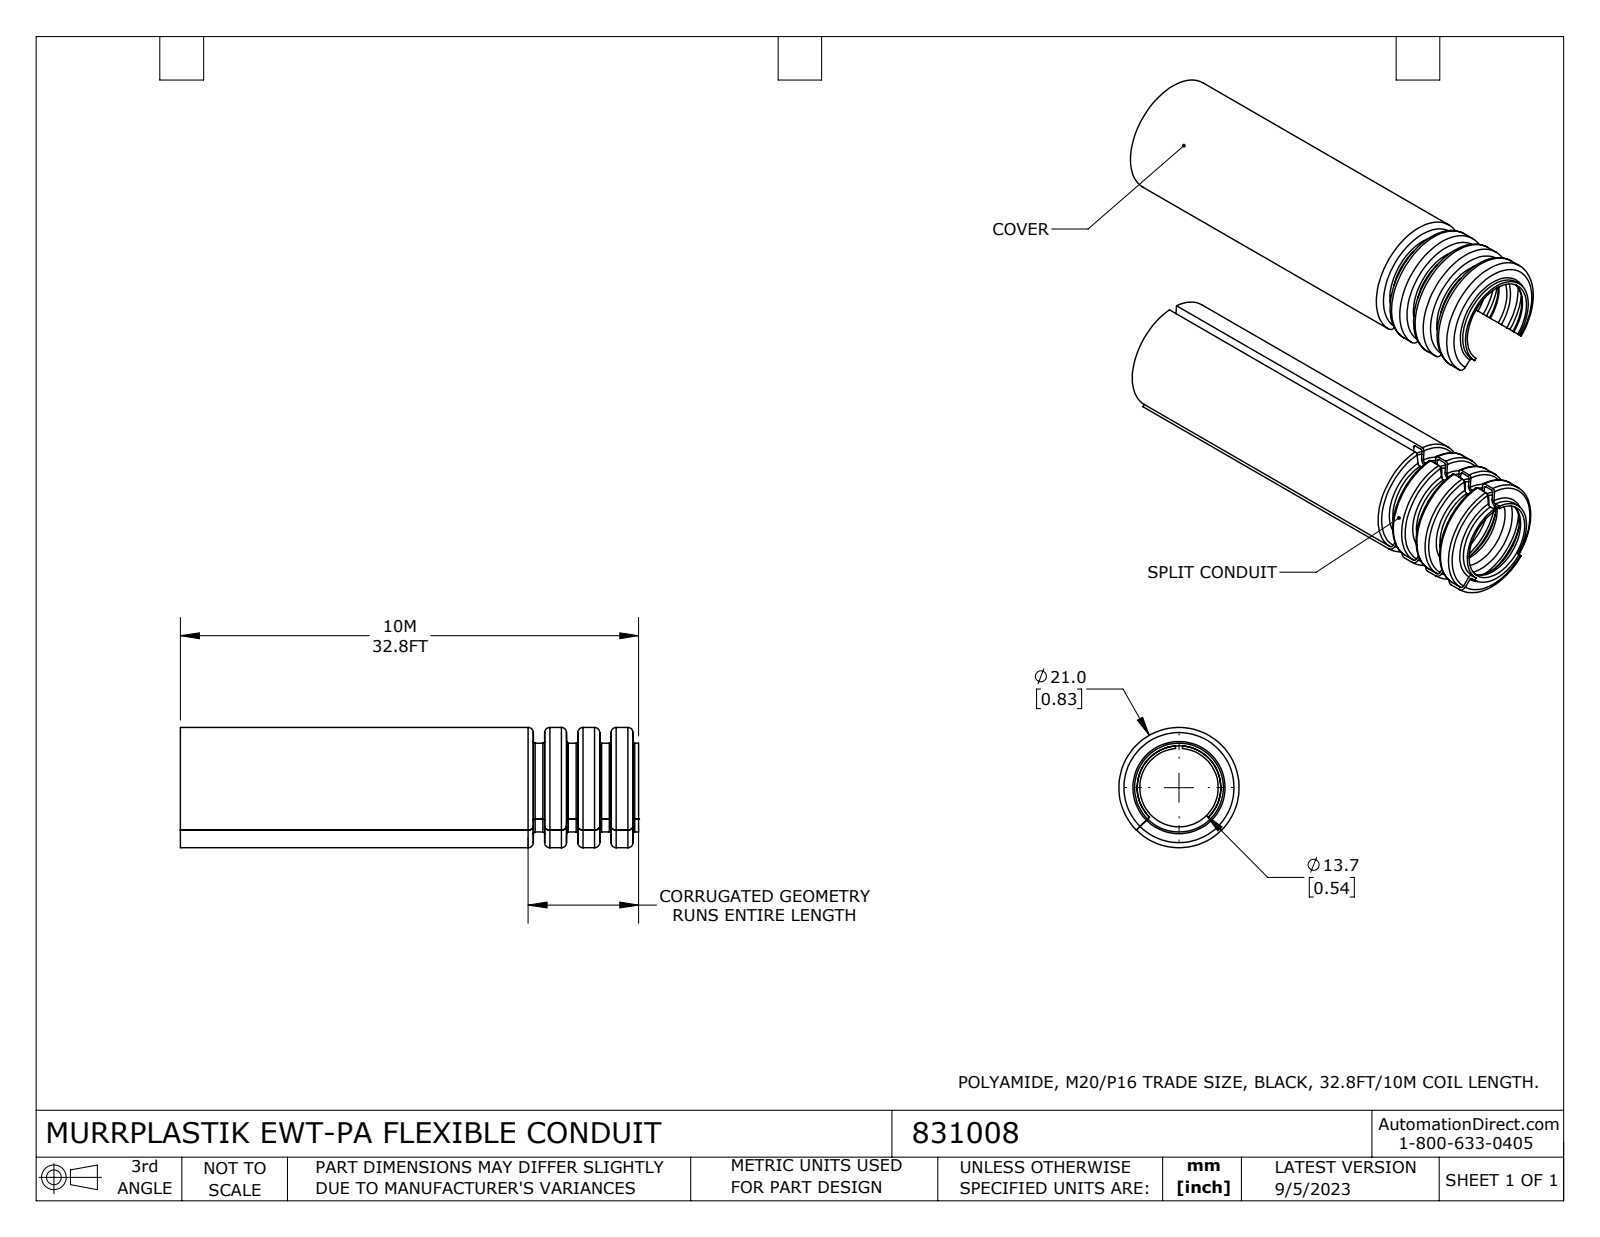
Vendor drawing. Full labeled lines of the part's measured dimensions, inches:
Part name (STEP PRODUCT): 831008
STEP written by: SolidWorks 2021 (CONFIG_CONTROL_DESIGN)
Units: inches
Bodies: 2 solids, 333 faces (10 planar, 107 cylindrical, 216 other)
Overall size (bounding box): 3.15 × 0.827 × 0.827
Volume: 0.808 in³ · Surface area: 30.6 in²
Round holes (diameter × count): ⌀0.539 ×1, ⌀0.756 ×1
Round bosses / shafts (diameter × count): ⌀0.827 ×1, ⌀0.61 ×1
Partial cylindrical surfaces — rounded edges, fillets, slot ends (radius × count): R0.287 ×1, R0.396 ×1
Main face-to-face distances: 3.15
